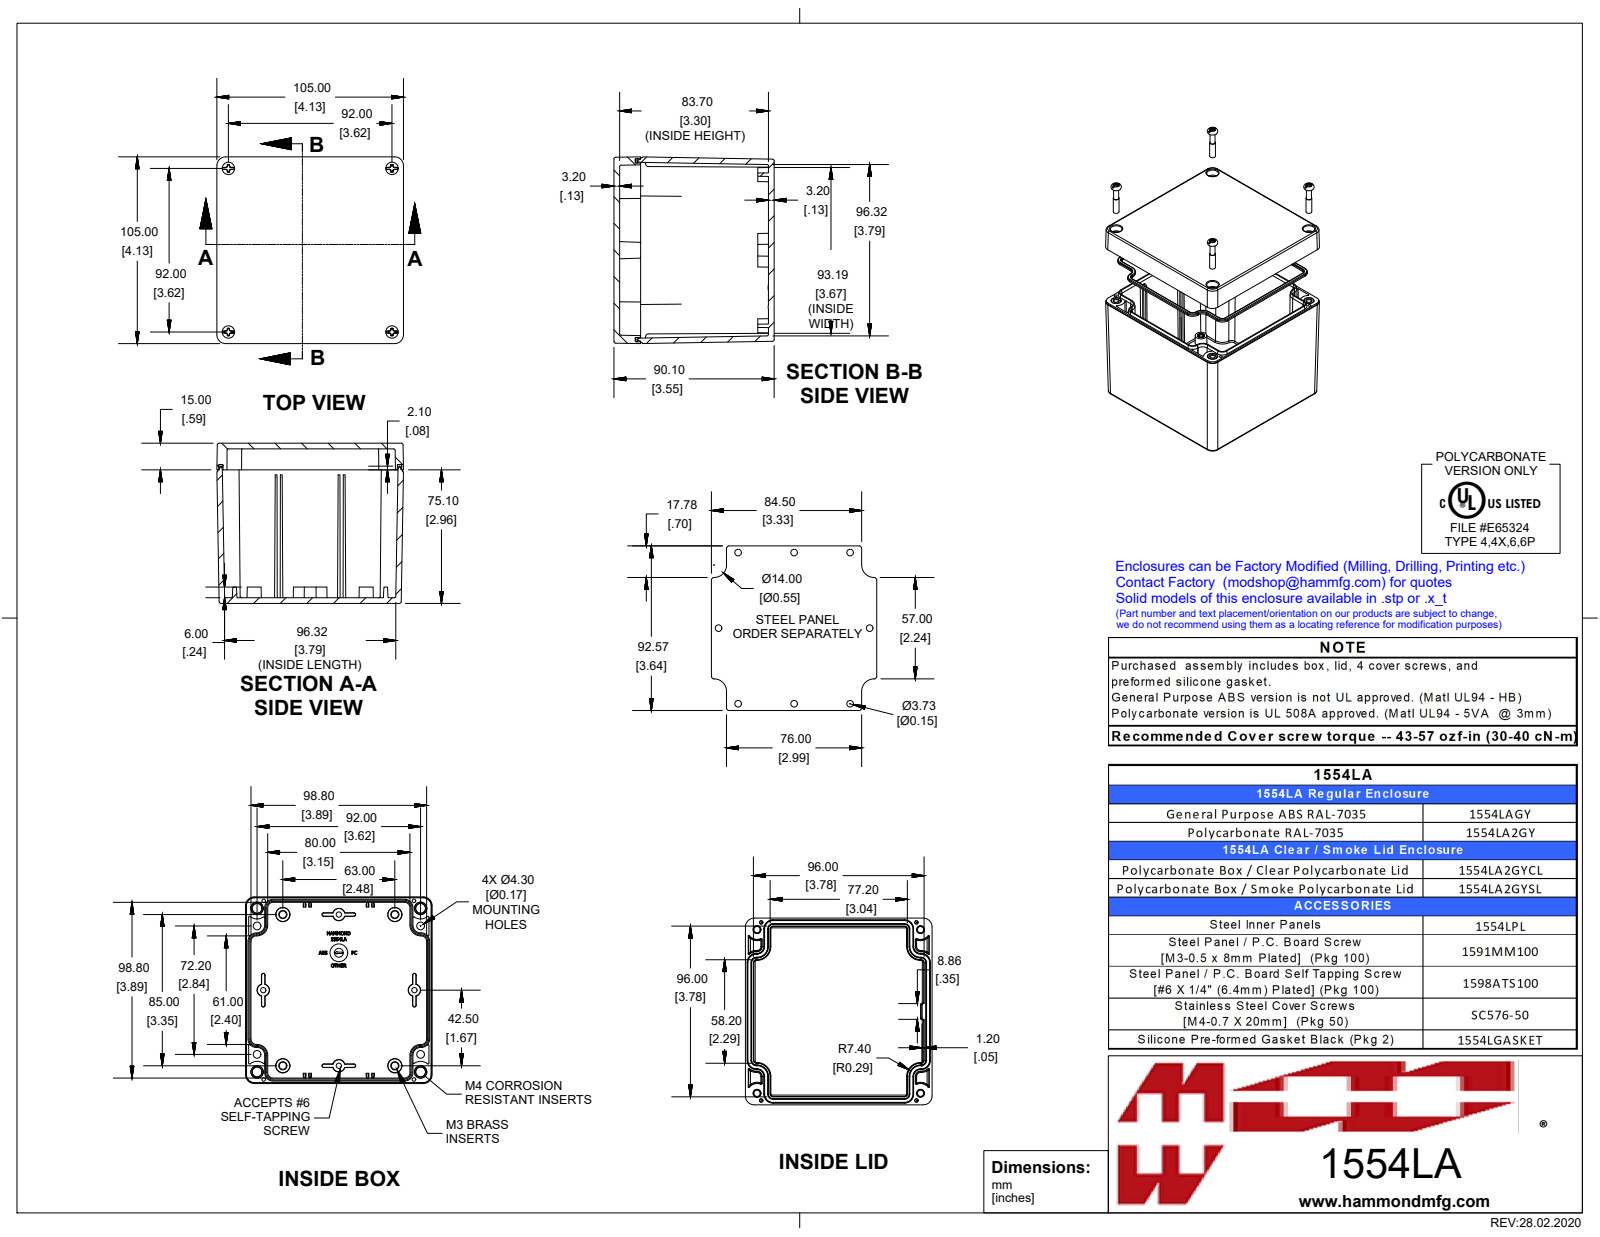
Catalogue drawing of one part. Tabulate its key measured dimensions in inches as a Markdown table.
| quantity | value |
| --- | --- |
| part name | 1554LAGY |
| STEP written by | SolidWorks 2019 (AUTOMOTIVE_DESIGN) |
| units | inches |
| bodies | 15 solids, 1858 faces (623 planar, 374 cylindrical, 861 other) |
| overall size | 4.134 × 4.134 × 3.547 |
| volume | 12.48 in³ |
| surface area | 219 in² |
| round holes (diameter × count) | 0.097 × 4, 0.128 × 4, 0.181 × 4 |
| round bosses / shafts (diameter × count) | 0.25 × 4, 0.218 × 4, 0.21 × 4, 0.19 × 4, 0.154 × 4, 0.153 × 4, 0.15 × 4, 0.135 × 4 |
| partial cylindrical surfaces (radius × count) | 0.02 × 26, 0.012 × 20, 0.039 × 12, 0.031 × 10, 0.104 × 8, 0.197 × 8, 0.199 × 8, 0.118 × 4 |
| main face-to-face distances | 0.122, 0.126, 3.421, 3.547, 3.295, 4.134, 4.012, 3.957, 3.835, 0.177 |
| hole center spacings | 0.587, 3.054, 3.531, 3.622, 4.631, 2.48, 3.346, 4.165 |
